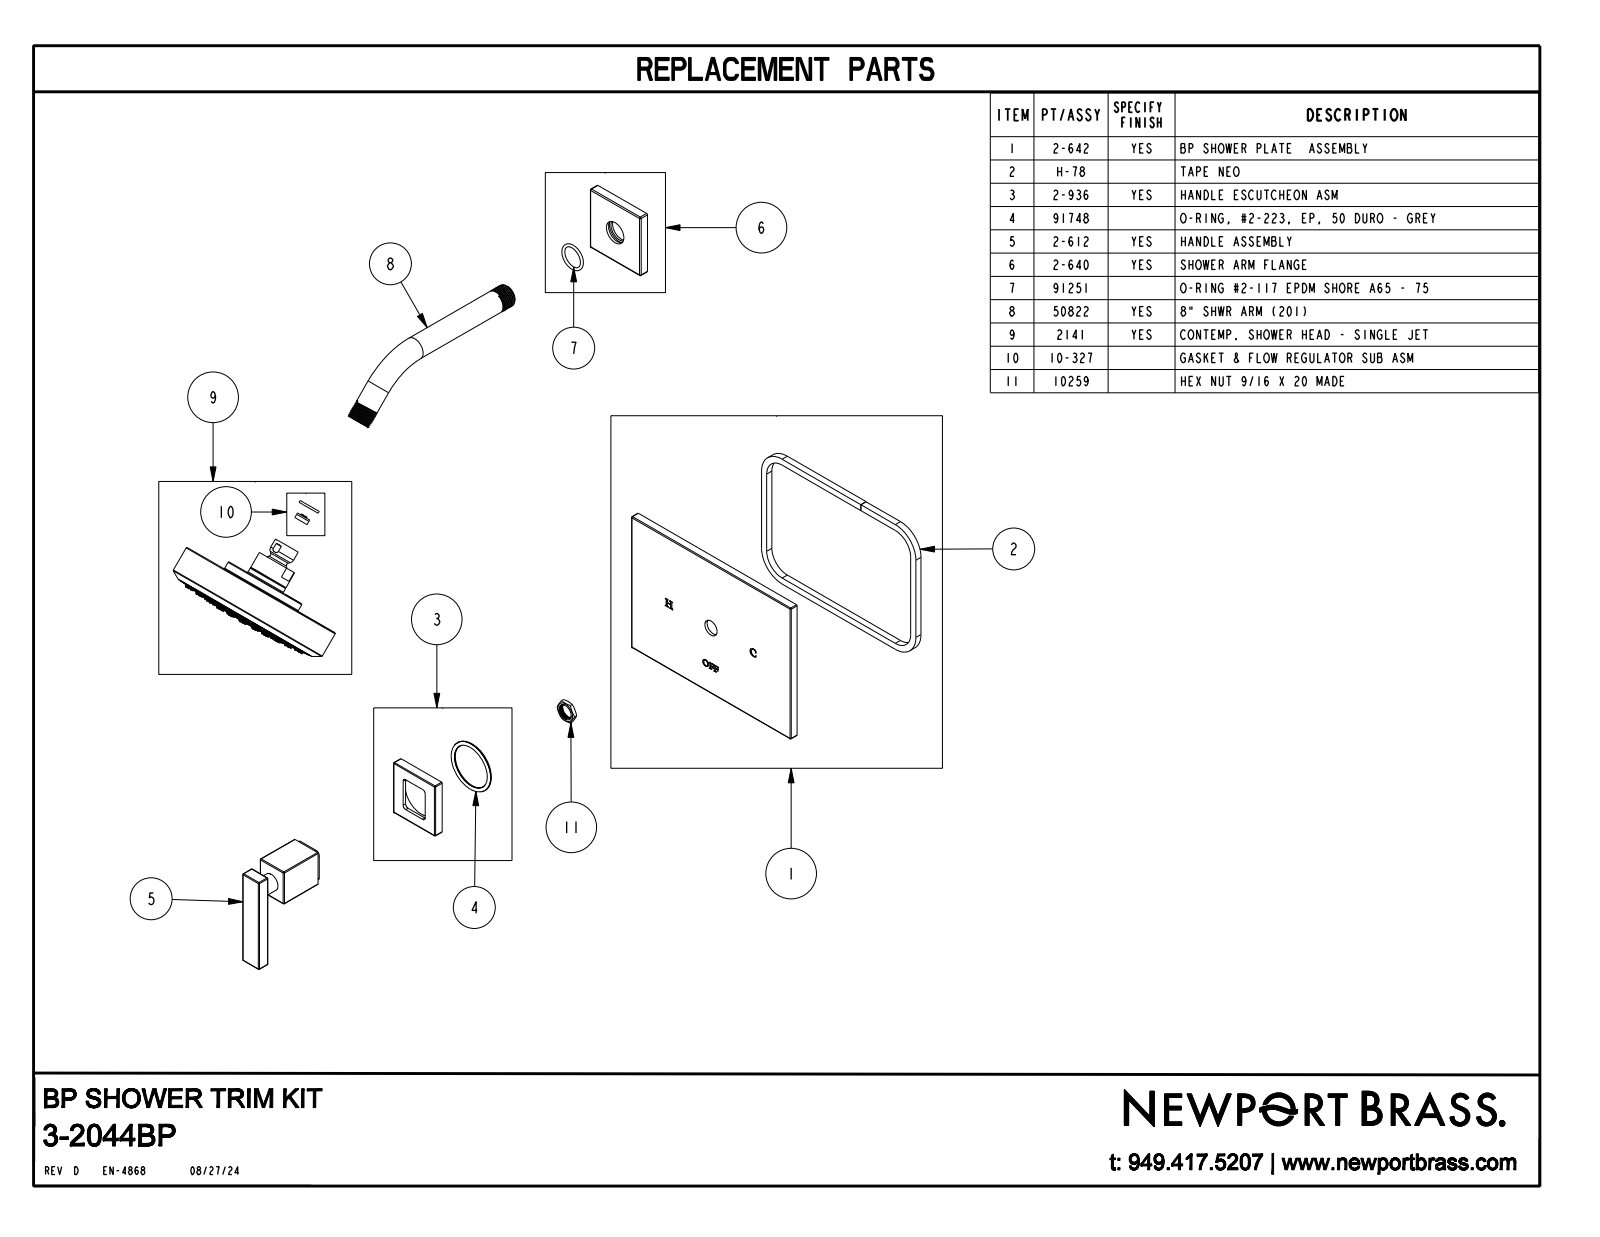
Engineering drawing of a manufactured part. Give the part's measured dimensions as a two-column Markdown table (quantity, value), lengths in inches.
| quantity | value |
| --- | --- |
| part name | 3-2044BP |
| STEP written by | CREO PARAMETRIC BY PTC INC, 2018400 (CONFIG_CONTROL_DESIGN) |
| units | inches |
| bodies | 2 solids, 1173 faces (174 planar, 256 cylindrical, 743 other) |
| overall size | 14.852 × 10.286 × 7.75 |
| volume | 58.58 in³ |
| surface area | 233.2 in² |
| round holes (diameter × count) | 0.05 × 90, 0.22 × 1, 5.256 × 1 |
| round bosses / shafts (diameter × count) | 1.4 × 2, 0.813 × 2, 5.91 × 1, 5.22 × 1, 2.92 × 1, 0.905 × 1, 0.65 × 1, 0.523 × 1 |
| partial cylindrical surfaces (radius × count) | 0.03 × 36, 0.04 × 8 |
| main face-to-face distances | 0.31, 0.35, 0.04, 0.291, 3.295, 4.455, 3.475, 4.275, 0.18, 0.98 |
| hole center spacings | 0.98, 1.41, 0.43, 1.343, 1.482, 1.893, 0.49, 0.55 |
